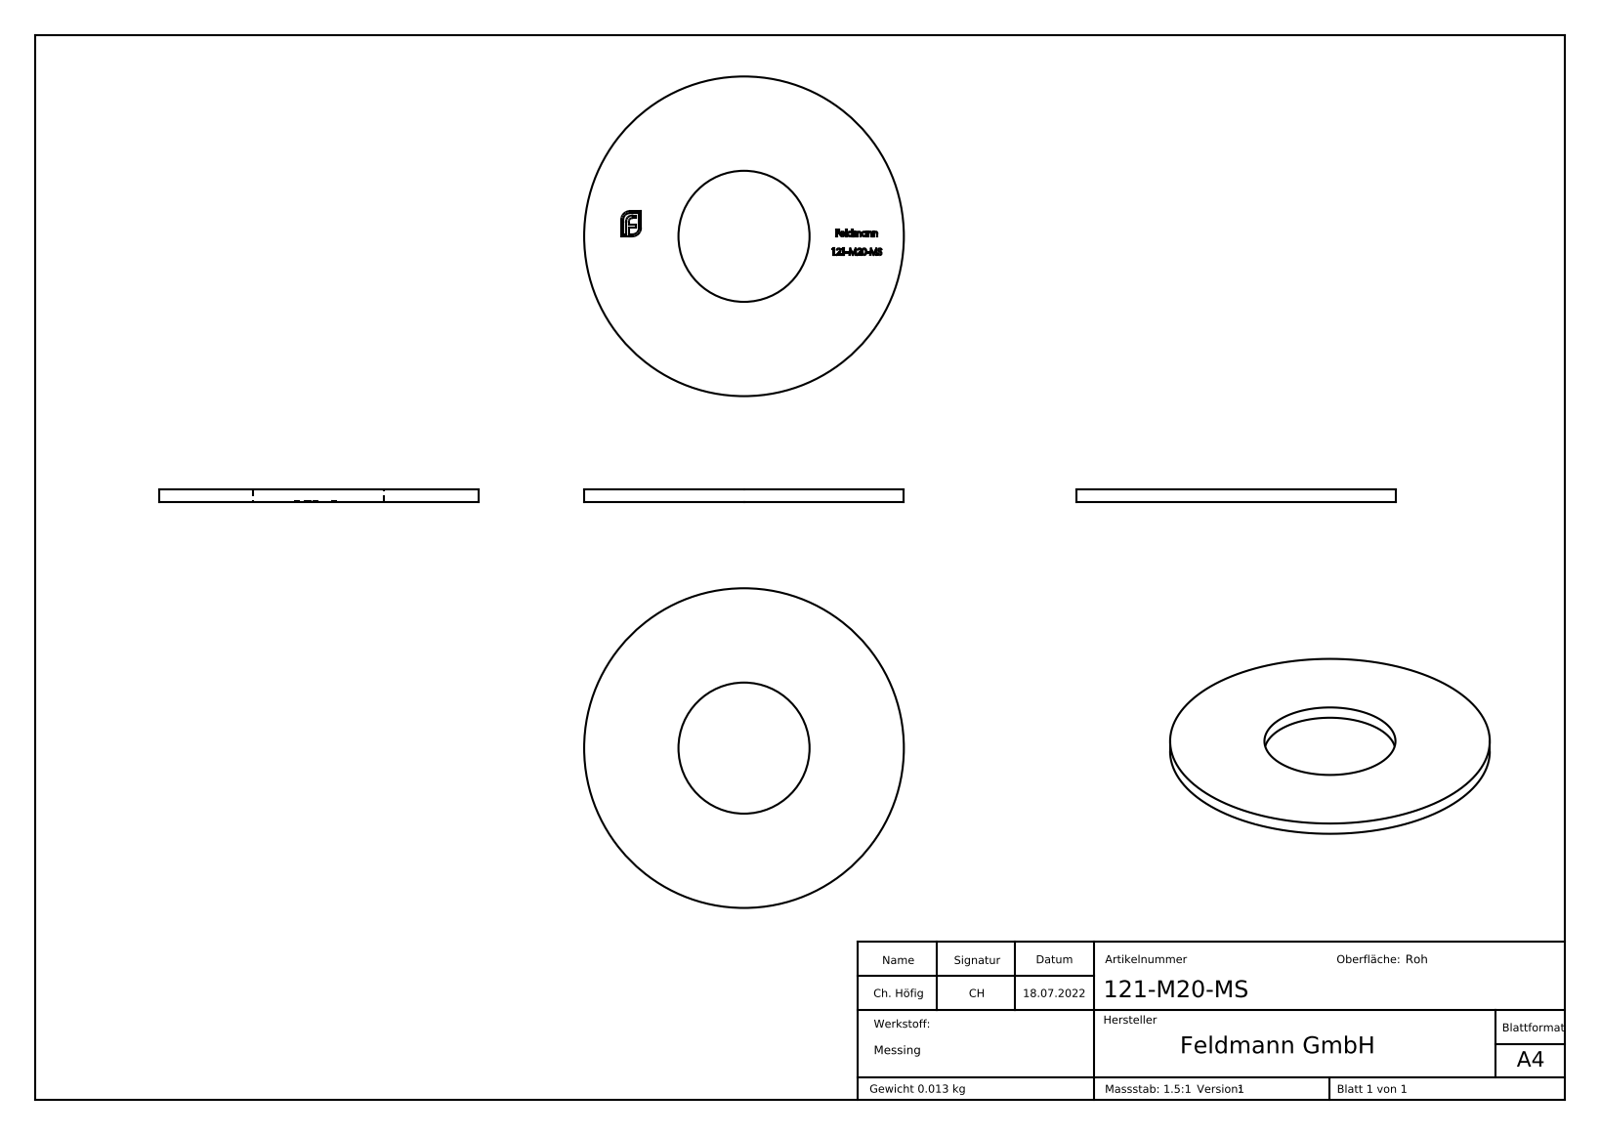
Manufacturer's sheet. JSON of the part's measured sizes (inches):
{"part_name": "121-M20-MS", "step_written_by": "SolidWorks 2018 (CONFIG_CONTROL_DESIGN)", "units": "inches", "bodies": {"solids": 1, "faces": 267, "planar": 161, "cylindrical": 2, "other": 104}, "overall_size": [1.575, 1.575, 0.059], "volume_in3": 0.096, "surface_area_in2": 3.666, "round_holes": [[0.646, 1]], "round_bosses_or_shafts": [[1.575, 1]], "face_to_face_distances": [0.059, 0.055, 0.091, 0.013, 0.101, 0.096, 0.013, 0.087, 1.022, 0.045]}
